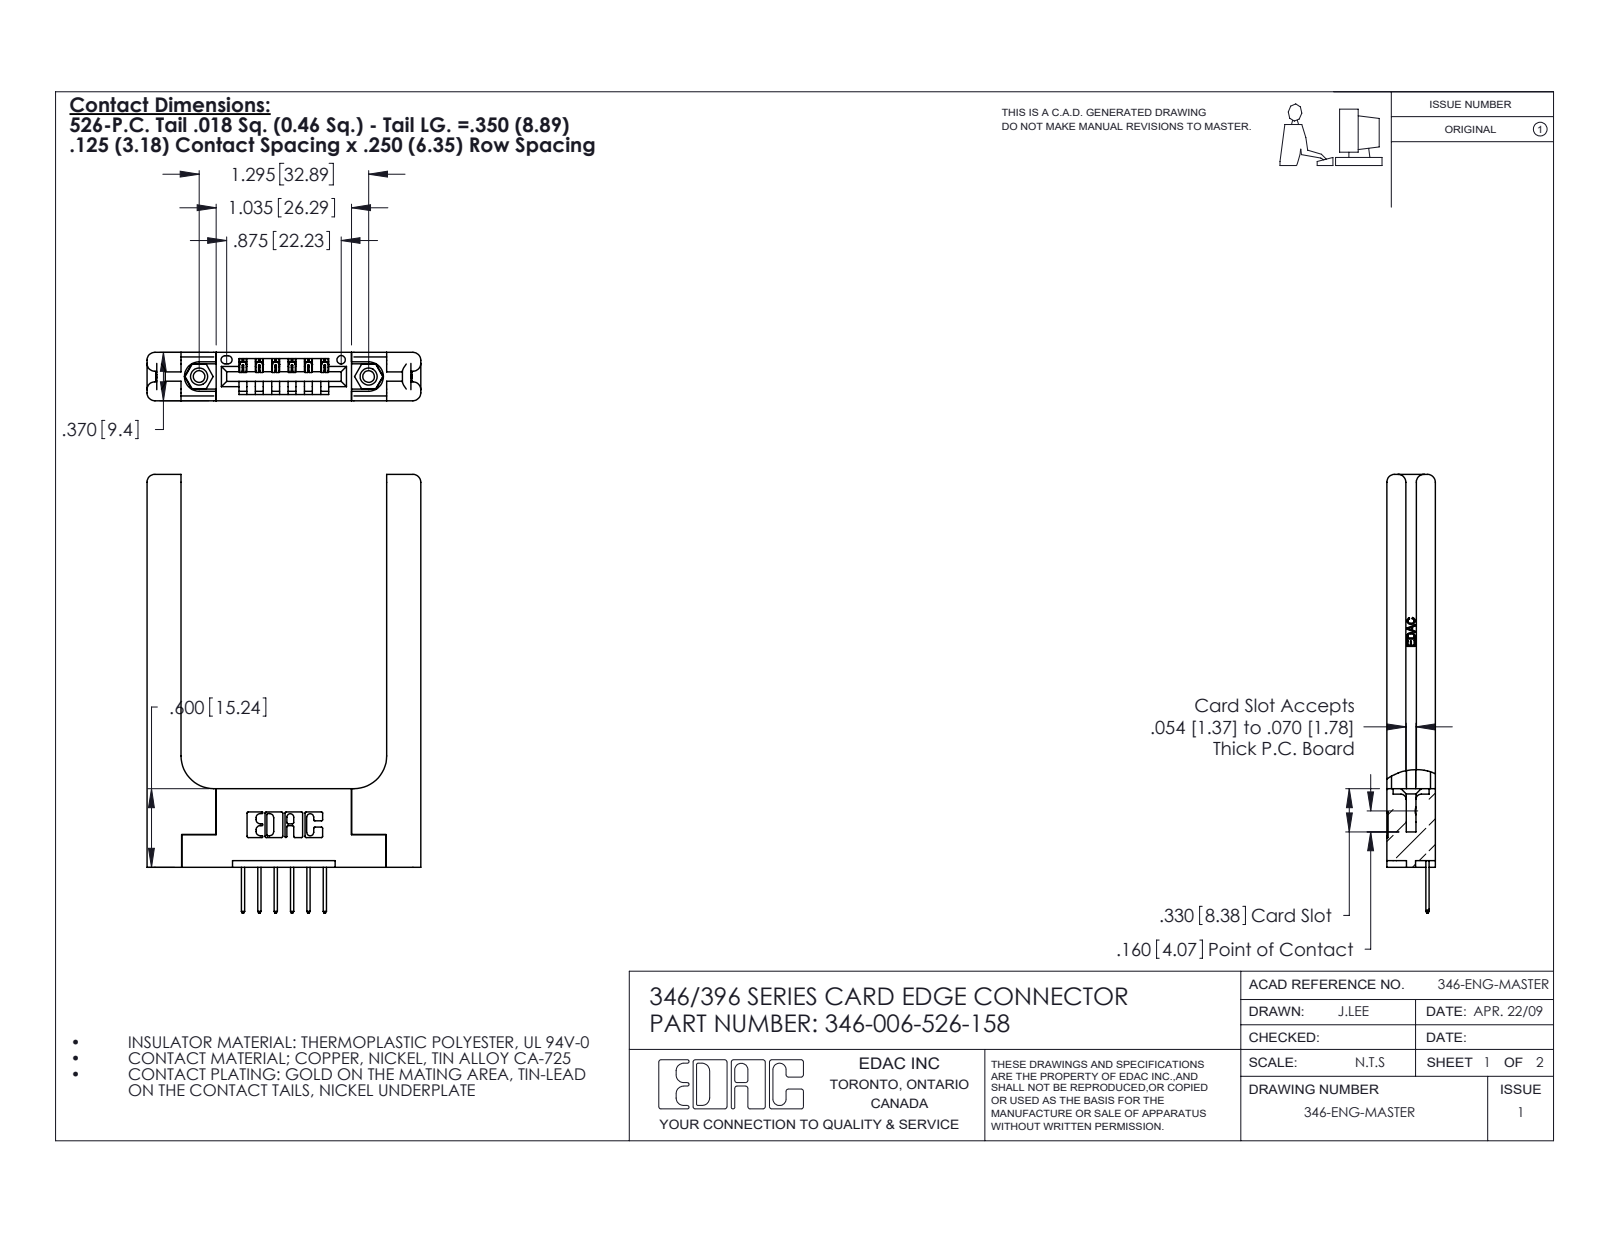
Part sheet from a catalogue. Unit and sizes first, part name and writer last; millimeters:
Units: millimetres
Overall size (bounding box): 85.1 × 53.1 × 9.4
Round holes (diameter × count): ⌀2.3 ×2, ⌀3.2 ×2, ⌀4 ×2, ⌀1.6 ×1
Round bosses / shafts (diameter × count): ⌀3.9 ×2
Partial cylindrical surfaces — rounded edges, fillets, slot ends (radius × count): R0.3 ×22, R1.5 ×16, R0.2 ×12, R0.3 ×12, R0.2 ×6, R0.8 ×6, R0.7 ×3, R0.8 ×2
Main face-to-face distances: 9.4, 3.8, 5.6, 1.8, 6.4, 3.8, 39.9, 1.8, 1.2, 8.2
Hole centre spacings: 6.2, 27.7, 32.9
Volume: 12 300 mm³ · Surface area: 10 830 mm²
Bodies: 11 solids, 740 faces (478 planar, 202 cylindrical, 60 other)
Part name (STEP PRODUCT): 345-250-001_345-250-001-102; 346 Part_Flush Mounting Lugs - 0.156 Dia-TH; 346-006-526-158; 345-292-001_345-293-126 (+1 more)
STEP written by: SolidWorks 2020 (CONFIG_CONTROL_DESIGN)
